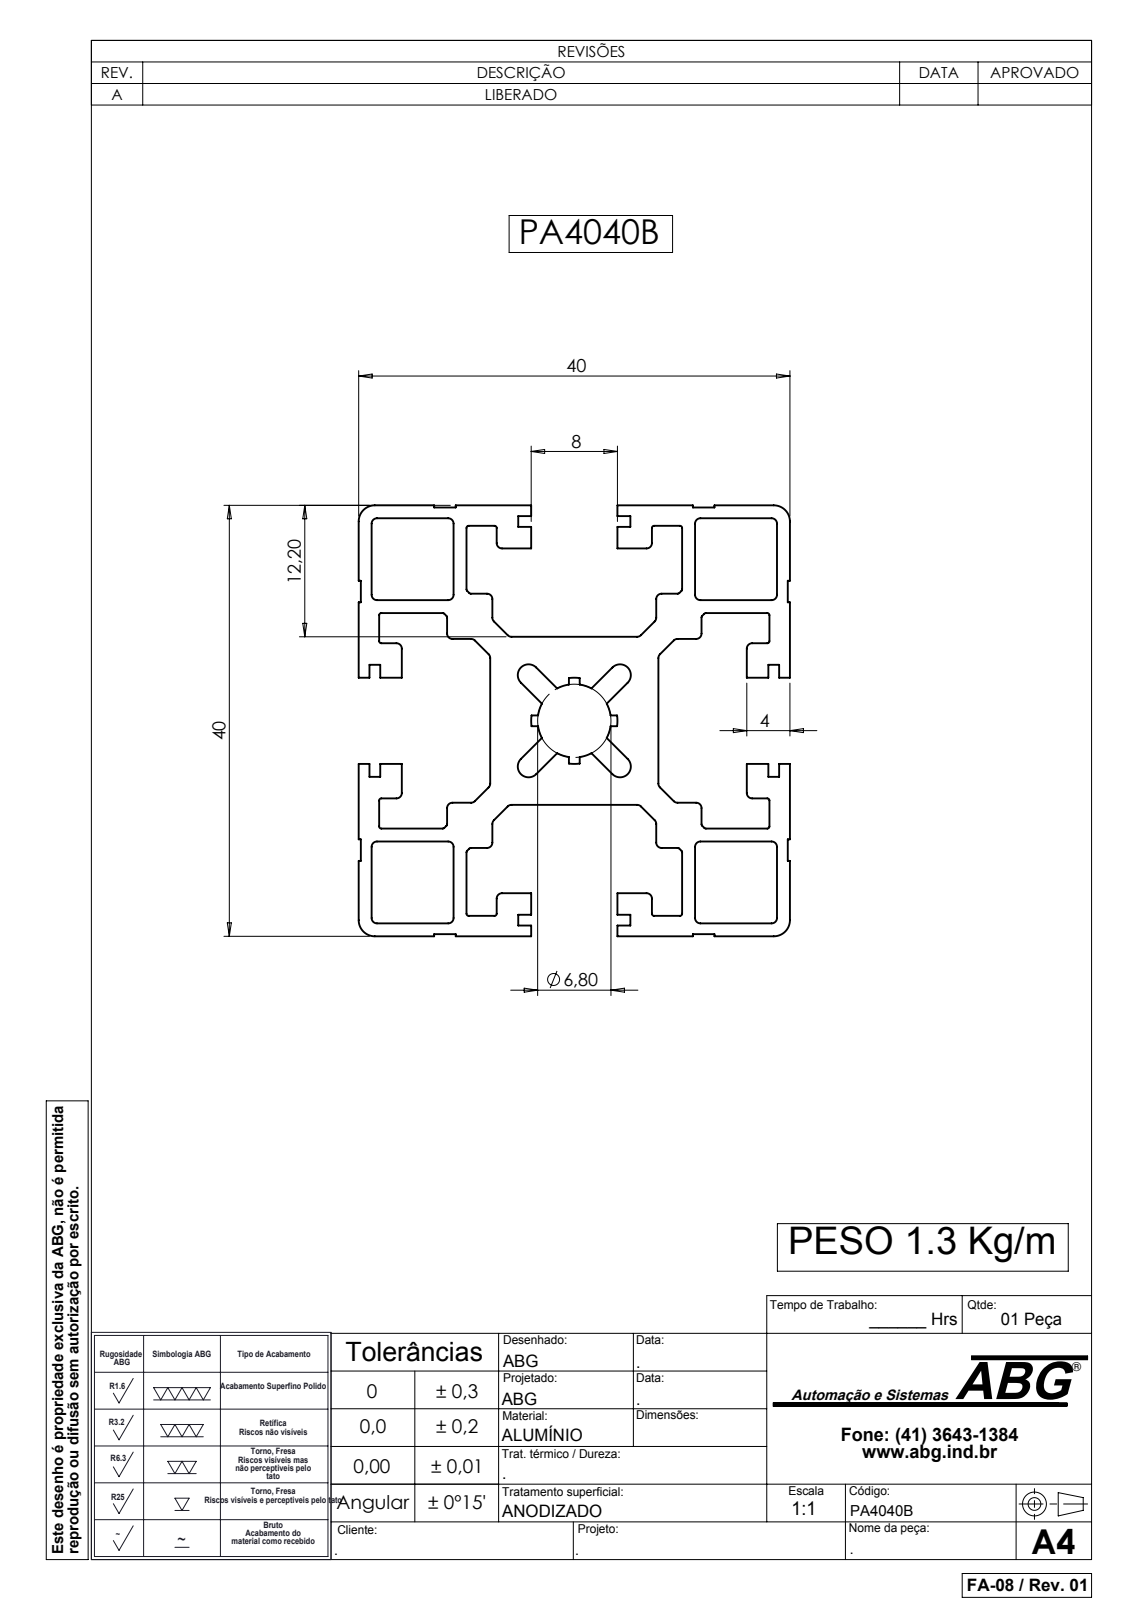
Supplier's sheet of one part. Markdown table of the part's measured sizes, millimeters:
| quantity | value |
| --- | --- |
| part name | PA4040B |
| STEP written by | SolidWorks 2007 (CONFIG_CONTROL_DESIGN) |
| units | millimeters |
| bodies | 1 solid, 285 faces (182 planar, 103 cylindrical, 0 other) |
| overall size | 6000 × 40 × 40 |
| volume | 3 266 000 mm³ |
| surface area | 3 383 000 mm² |
| partial cylindrical surfaces (radius × count) | 0.5 × 48, 0.2 × 32, 1 × 4, 1.5 × 4, 3.4 × 1, 4 × 1 |
| main face-to-face distances | 1.2, 8.8, 30, 12.2, 31.2, 38.8, 7.6, 40, 27.8, 11 |
